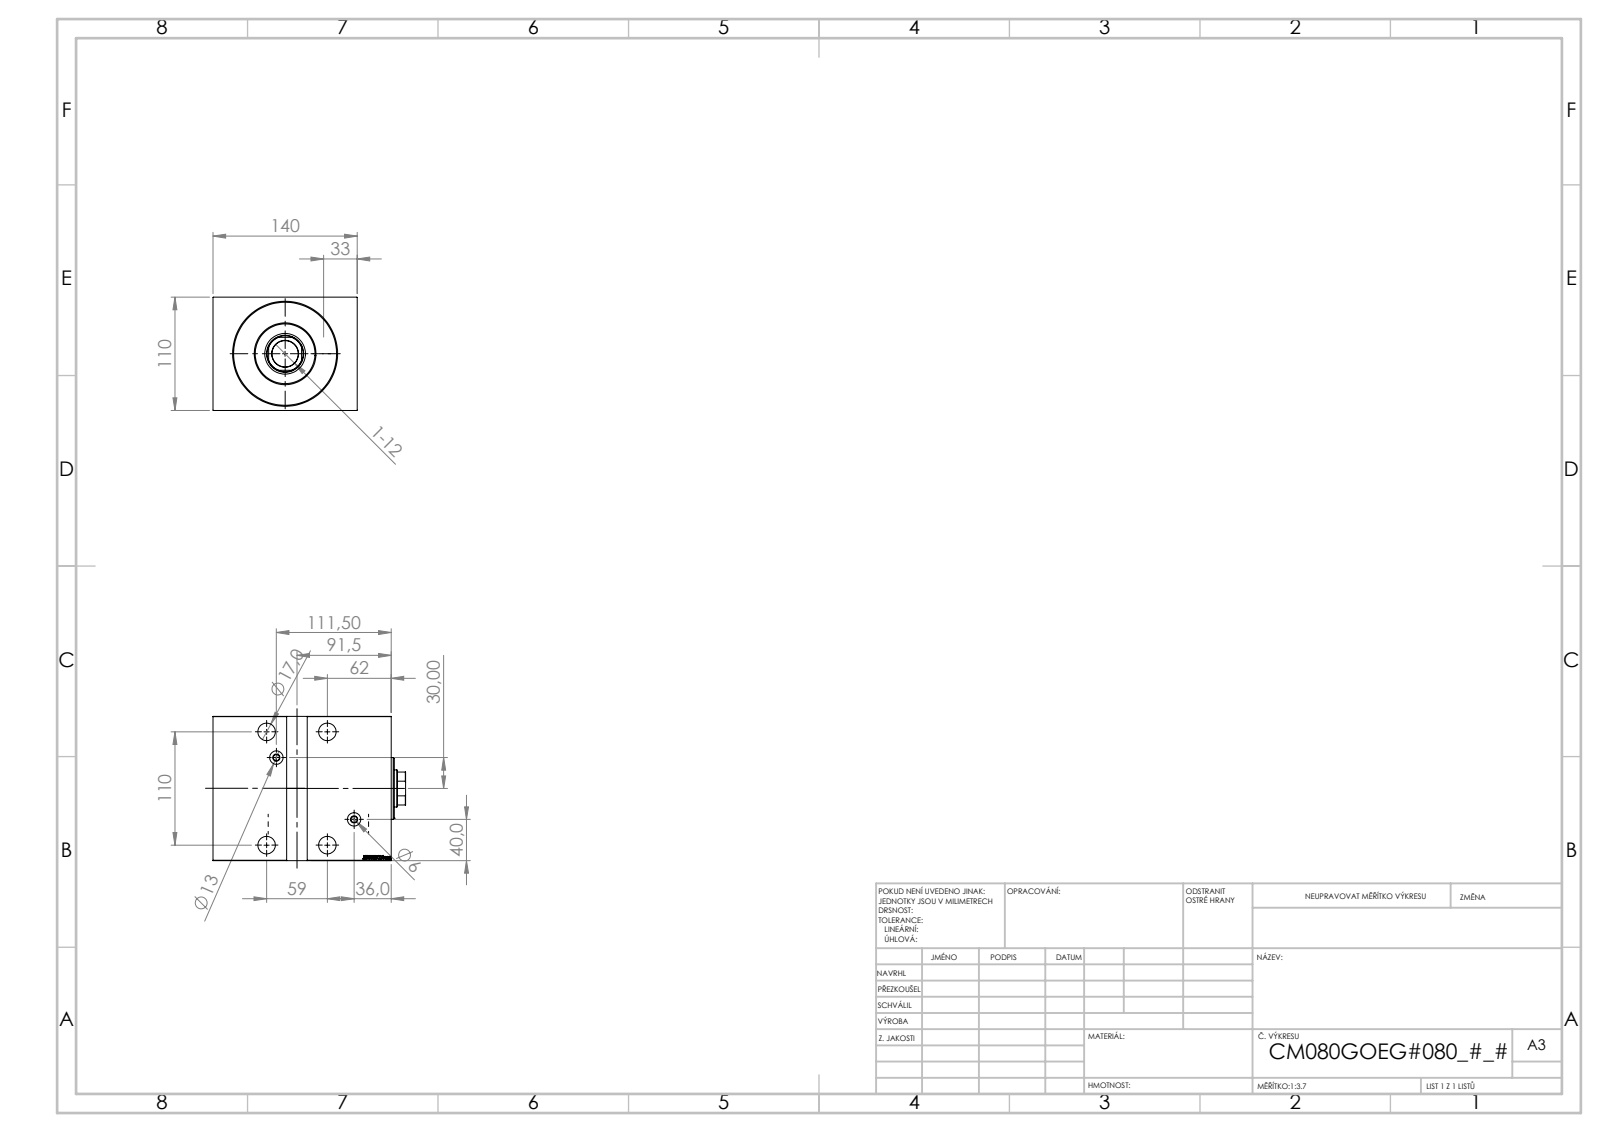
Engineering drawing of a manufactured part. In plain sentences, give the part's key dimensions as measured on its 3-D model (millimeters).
The part is named "V450CM_G_VCP; V450CM_VC_G; V450CM_G_Body; Zatka_OIL_PORT". Its 3-D file was written by "SolidWorks 2019 (CONFIG_CONTROL_DESIGN)". It is 5 solids with 896 faces: 442 planar, 56 cylindrical and 398 other. Overall it measures 187 by 140 by 110 millimeters. Its volume is 2 169 000 cubic millimeters and its surface area 240 439 square millimeters. Round holes: 4 of diameter 17, 4 of diameter 25, 2 of diameter 6, 2 of diameter 13, 1 of diameter 25.5, 1 of diameter 36, 1 of diameter 39.5, 1 of diameter 80, 1 of diameter 82, 1 of diameter 100. Round bosses or shafts: 2 of diameter 26, 2 of diameter 7, 1 of diameter 60. Partial cylindrical surfaces (rounded edges, fillets, slot ends): 1 of radius 17.5. The main face-to-face distances are 110, 140, 5, 173, 21, 152, 168, 147, 79, 58. The hole center spacings are 59, 110, 124.82, 26.74, 36.07, 55.45, 85.53, 88.6.
